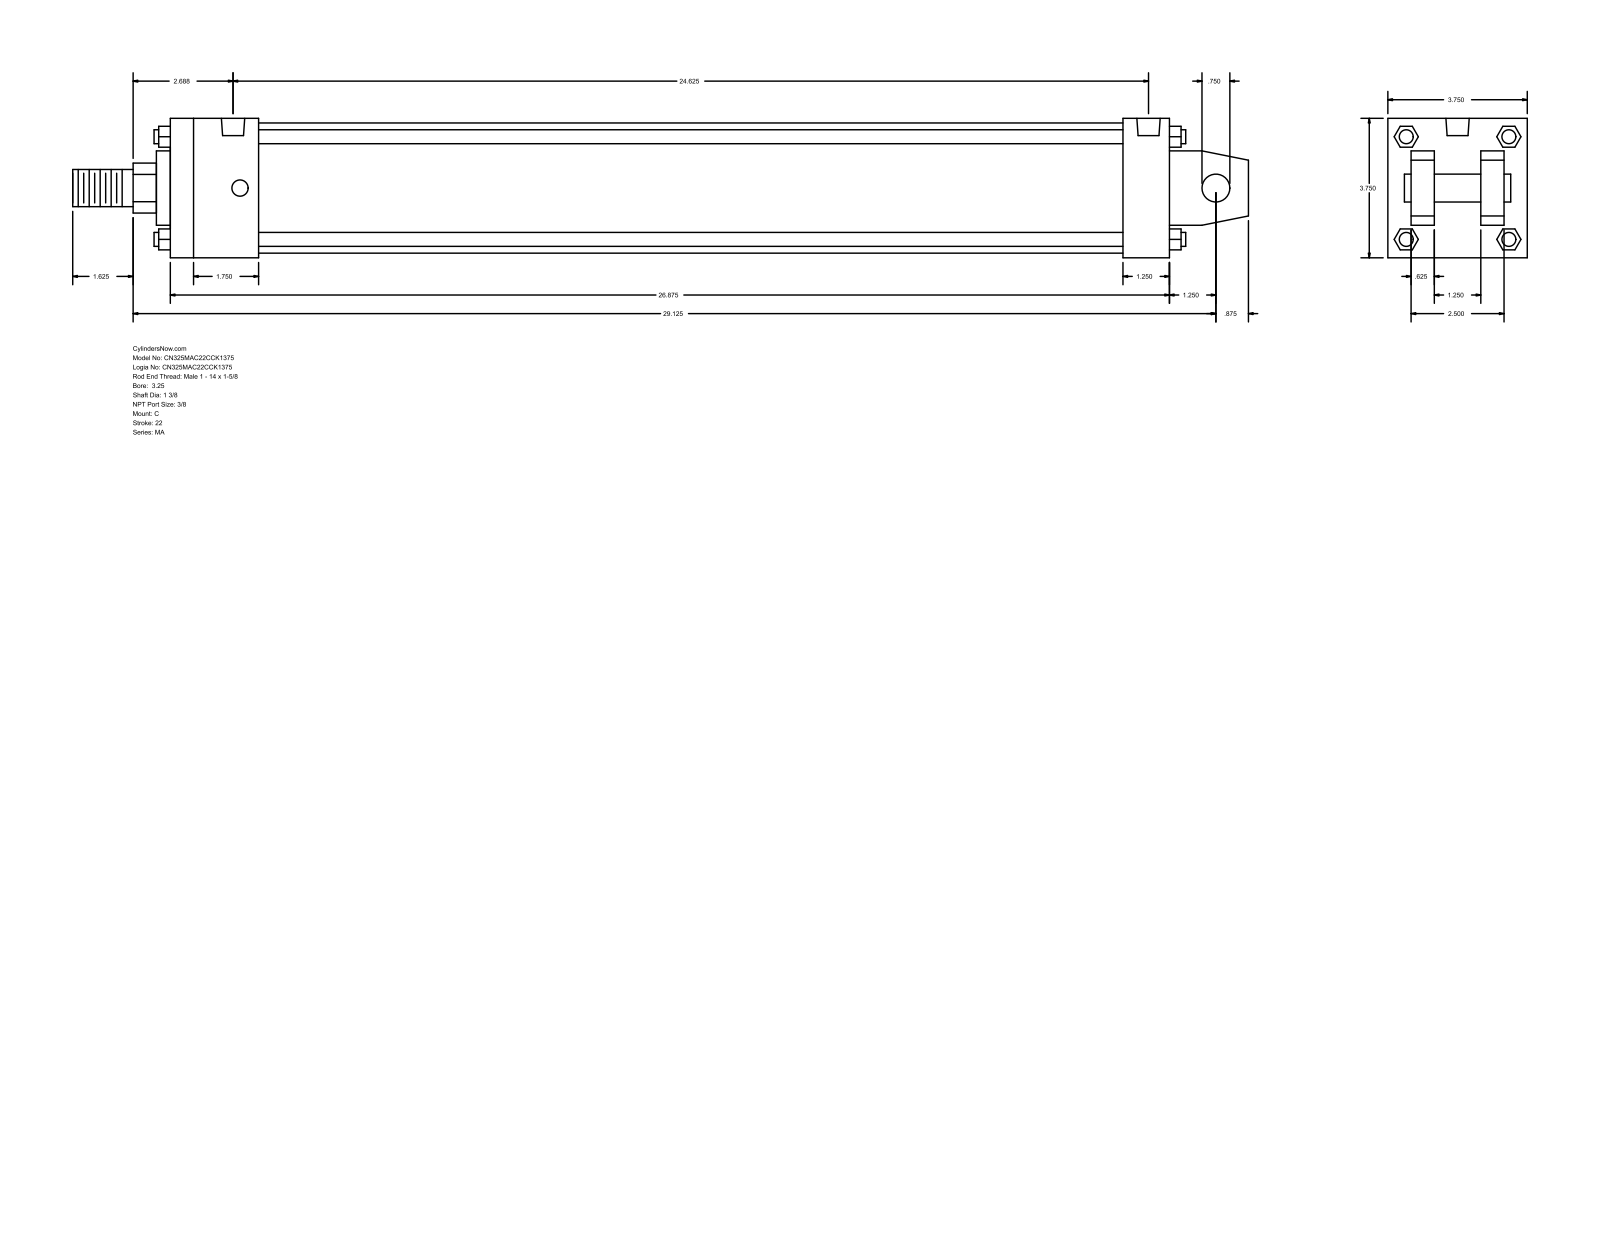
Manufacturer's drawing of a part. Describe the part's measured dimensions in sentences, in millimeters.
The part is named "MA_C__0325_1.375". Its 3-D file was written by "GSSL Pune (CONFIG_CONTROL_DESIGN)". It is 0 solids with 139 faces: 108 planar, 31 cylindrical and 0 other. Overall it measures 803.27 by 95.25 by 95.25 millimeters. Round holes: 4 of diameter 11.11, 2 of diameter 15.93. Round bosses or shafts: 4 of diameter 9.53, 1 of diameter 88.9, 1 of diameter 50.8, 1 of diameter 34.92, 1 of diameter 25.4, 1 of diameter 19.05. Partial cylindrical surfaces (rounded edges, fillets, slot ends): 1 of radius 17.06. The main face-to-face distances are 95.24, 15.87, 63.5, 682.62, 31.74, 79.37, 47.63, 650.87, 31.75, 60.32. The hole center spacings are 615.95, 4.76, 4.77, 620.71, 620.72, 625.48.
